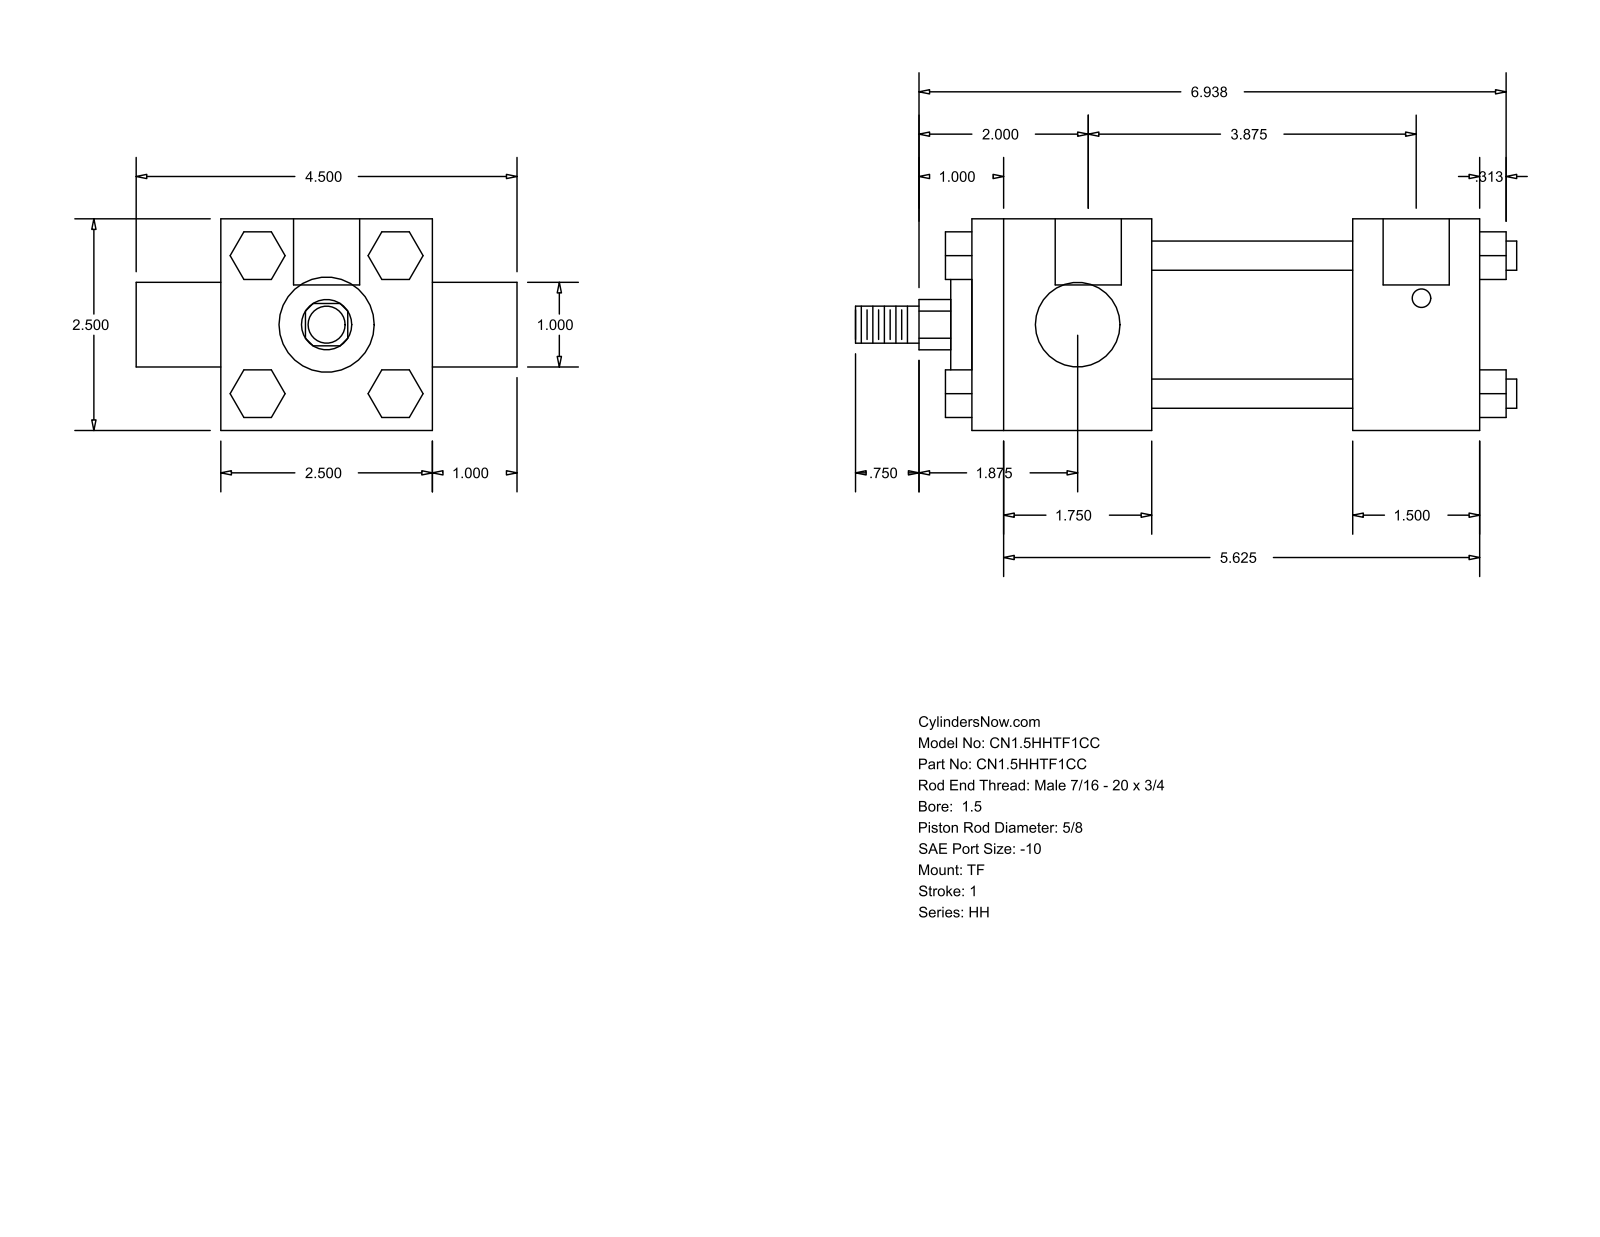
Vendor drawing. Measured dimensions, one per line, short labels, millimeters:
name: HH_TF__0150_0.625
written by: GSSL Pune (CONFIG_CONTROL_DESIGN)
unit: mm
bodies: 0 solids, 120 faces (92 planar, 28 cylindrical, 0 other)
size: 198.44 × 114.3 × 63.5
holes: 3× ⌀5.56, 2× ⌀19.84
bosses: 4× ⌀8.76, 1× ⌀44.45, 1× ⌀28.57, 1× ⌀25.4, 1× ⌀15.88, 1× ⌀11.11
rounds: 1× R7.54
face distances: 63.5, 114.3, 152.4, 38.1, 53.97, 98.43, 60.33, 25.4, 88.9, 20.7
hole spacings: 1.59, 100.01, 98.42, 101.6
